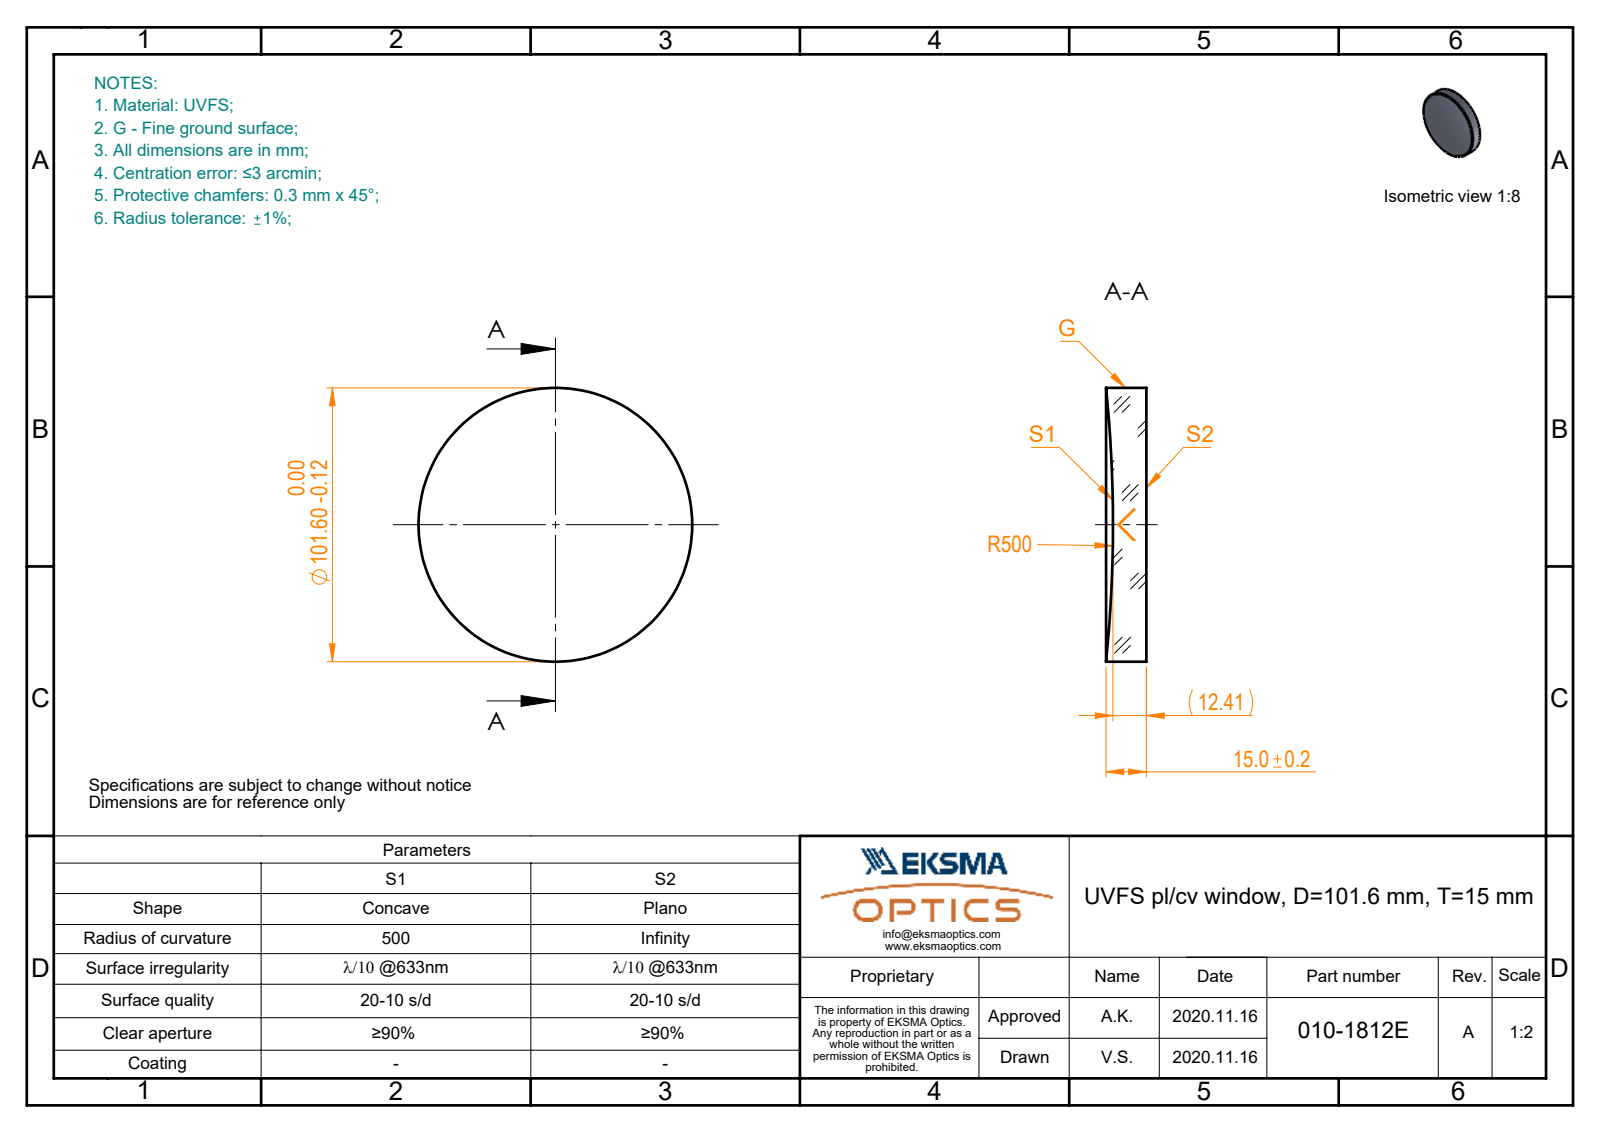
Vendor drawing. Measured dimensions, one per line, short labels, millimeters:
name: 010-1812E_UVFS_PCV_window
written by: SolidWorks 2019 (CONFIG_CONTROL_DESIGN)
unit: mm
bodies: 1 solid, 5 faces (1 planar, 2 cylindrical, 2 other)
size: 101.6 × 101.6 × 15
volume: 111 113 mm³; area: 21 023 mm²
bosses: 1× ⌀101.6
